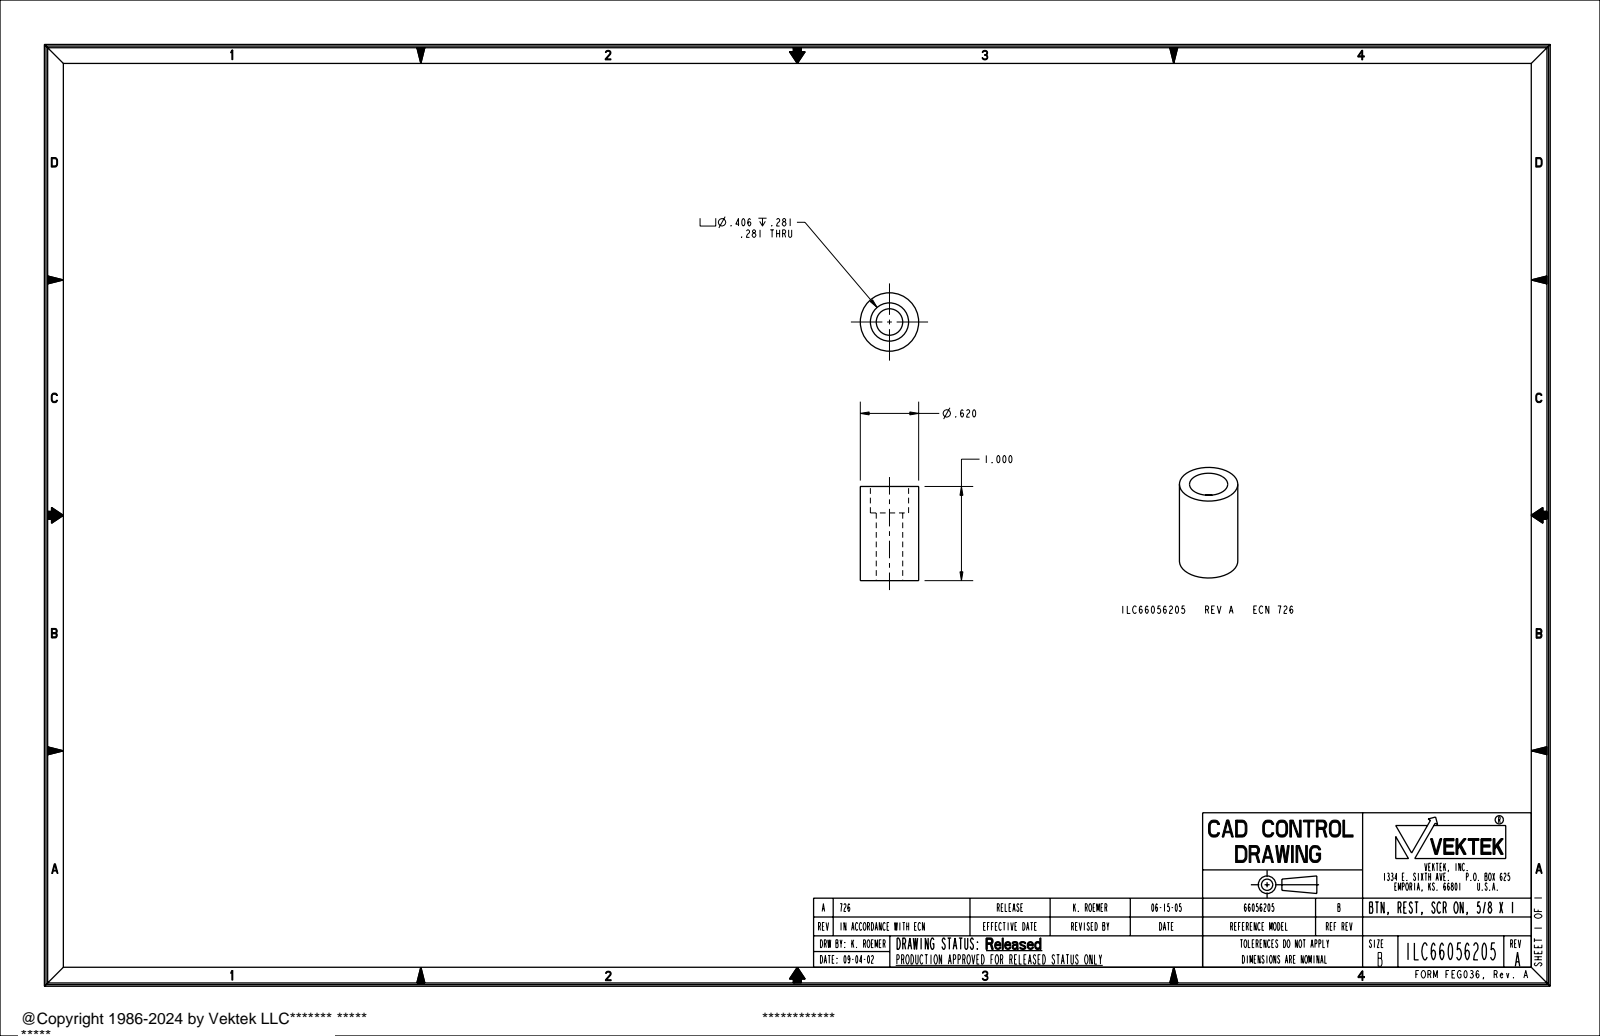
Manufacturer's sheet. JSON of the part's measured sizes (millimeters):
{"part_name": "ILC66056205", "step_written_by": "PRO/ENGINEER BY PARAMETRIC TECHNOLOGY CORPORATION, 2004290 (AUTOMOTIVE_DESIGN_CC2)", "units": "millimeters", "bodies": {"solids": 1, "faces": 9, "planar": 3, "cylindrical": 6, "other": 0}, "overall_size": [25.4, 15.7, 15.7], "volume_mm3": 3620, "surface_area_mm2": 2207, "round_holes": [[7.1, 1], [10.3, 1]], "round_bosses_or_shafts": [[15.7, 1]], "face_to_face_distances": [25.4, 18.3, 7.1]}
